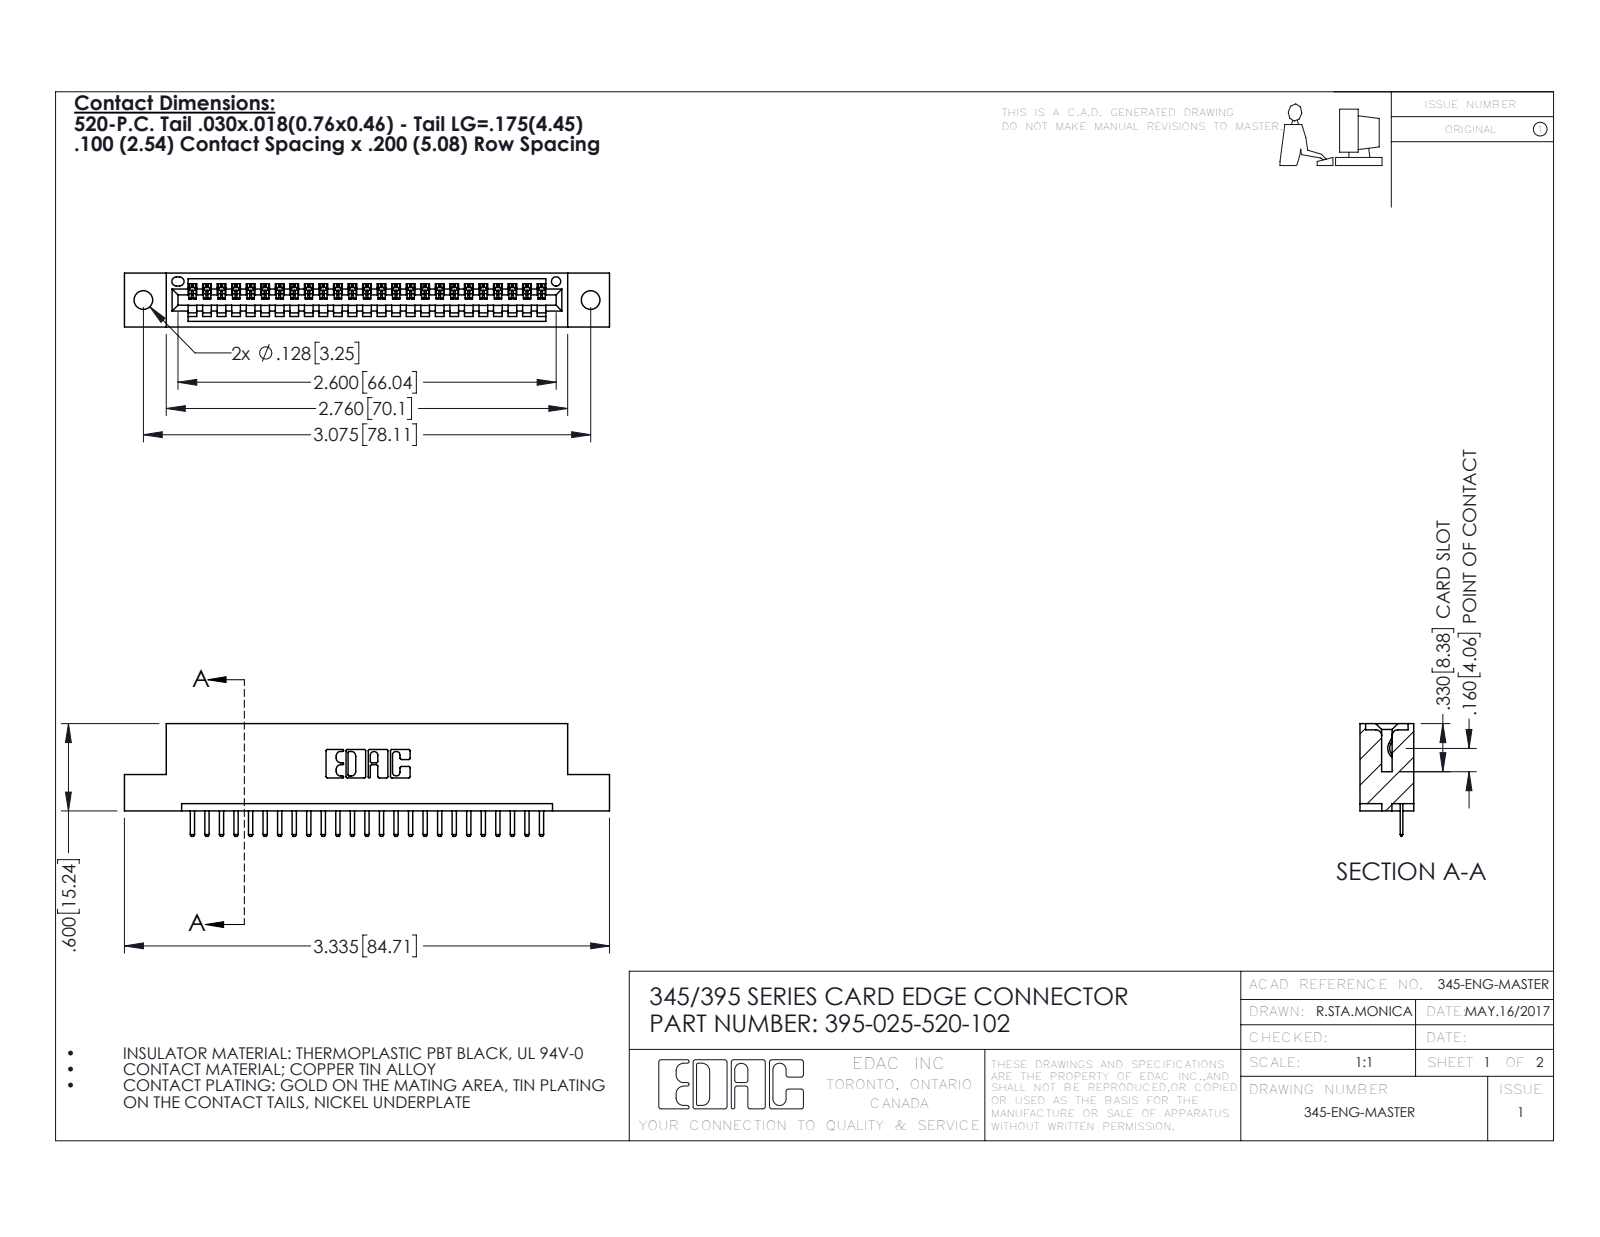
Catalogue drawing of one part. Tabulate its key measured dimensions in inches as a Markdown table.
| quantity | value |
| --- | --- |
| part name | 345-292-001_345-293-120; 345 Part_Flush Mounting Lugs - 0.128 Dia; 395-025-520-102 |
| STEP written by | SolidWorks 2016 (CONFIG_CONTROL_DESIGN) |
| units | inches |
| bodies | 26 solids, 1676 faces (1130 planar, 546 cylindrical, 0 other) |
| overall size | 3.335 × 0.775 × 0.37 |
| volume | 0.476 in³ |
| surface area | 14.92 in² |
| round holes (diameter × count) | 0.128 × 2, 0.064 × 1 |
| partial cylindrical surfaces (radius × count) | 0.01 × 52, 0.006 × 50, 0.01 × 22, 0.007 × 6, 0.031 × 6, 0.026 × 3, 0.031 × 2, 0.04 × 2 |
| main face-to-face distances | 0.298, 0.072, 0.37, 0.2, 0.098, 0.272, 0.025, 0.225, 0.072, 0.149 |
| hole center spacings | 0.27, 2.84, 3.075 |
